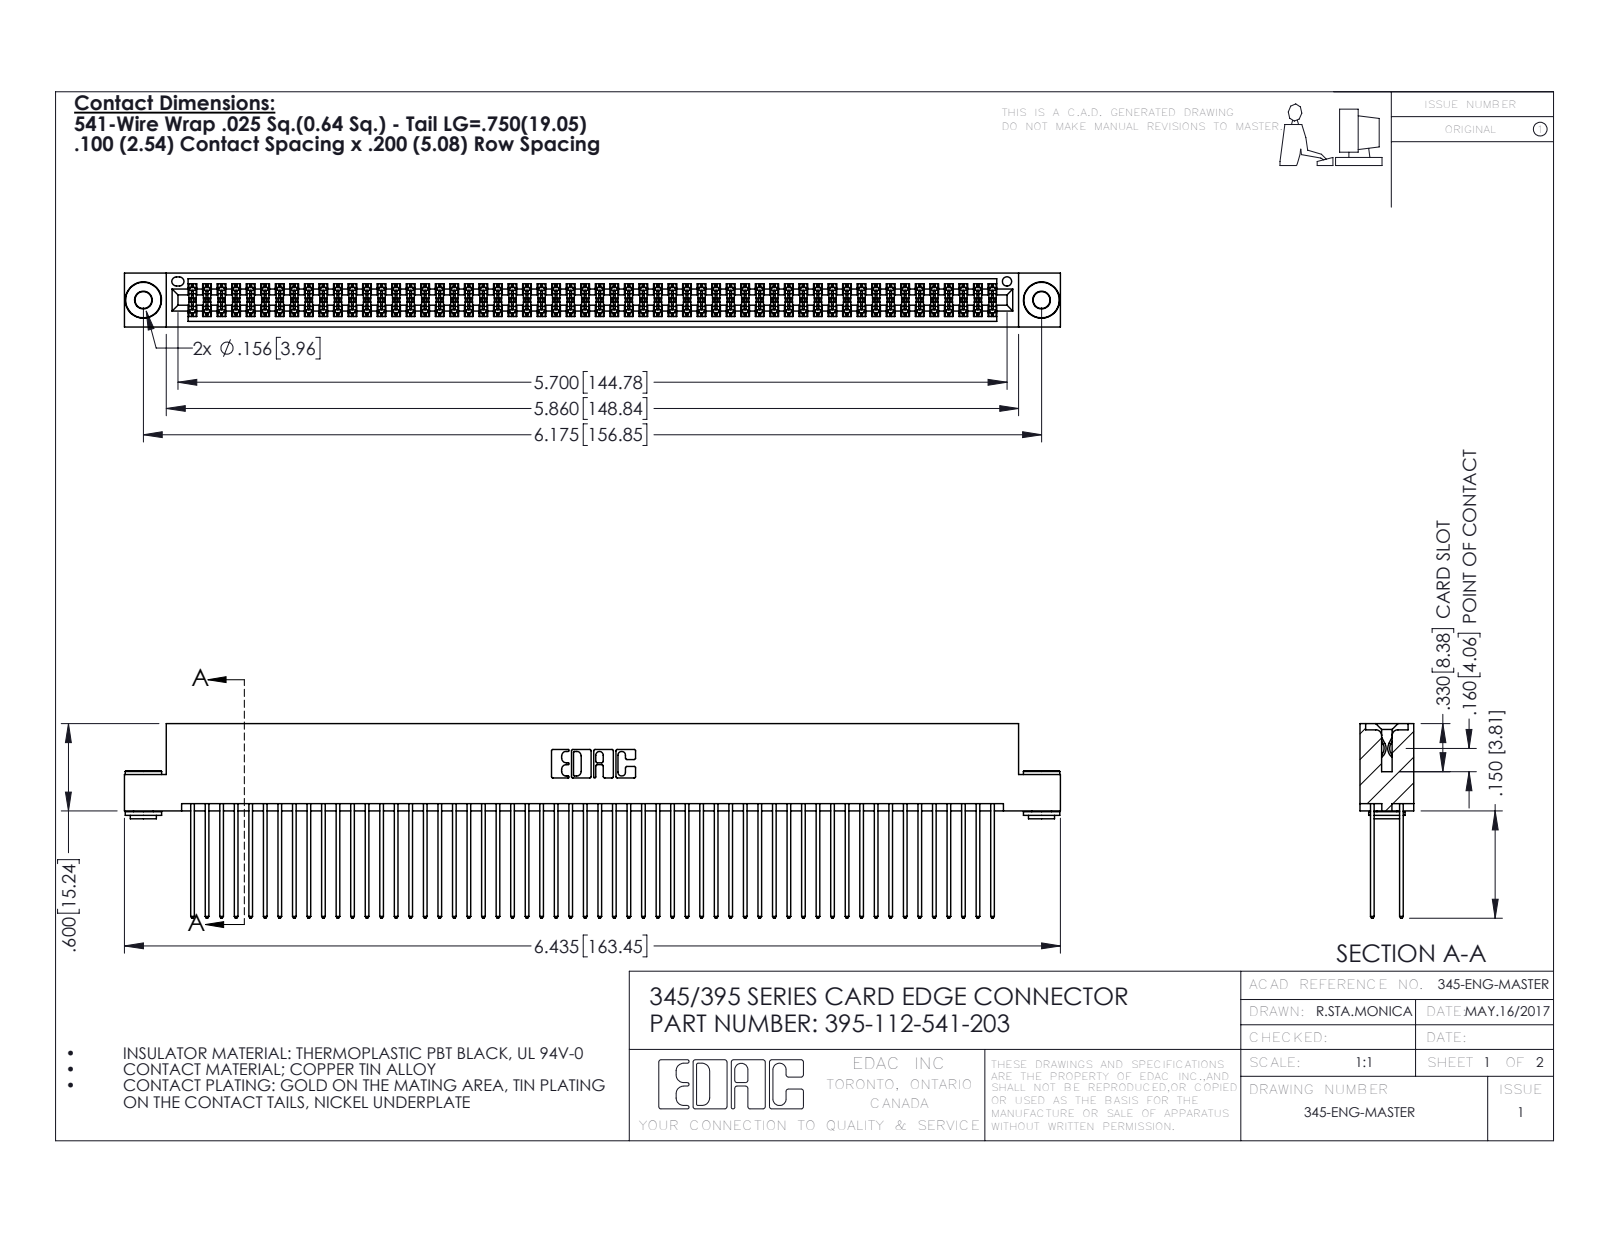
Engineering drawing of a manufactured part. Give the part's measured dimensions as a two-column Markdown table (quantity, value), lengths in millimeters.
| quantity | value |
| --- | --- |
| part name | 395-112-541-203; 345 Part_Flush Mounting Lugs - 0.156 Dia-TH; 345-250-002_345-250-002-102; 345-292-001_345-293-141 |
| STEP written by | SolidWorks 2016 (CONFIG_CONTROL_DESIGN) |
| units | millimeters |
| bodies | 115 solids, 5764 faces (3786 planar, 1970 cylindrical, 8 other) |
| overall size | 163.4 × 34 × 9.4 |
| volume | 16 670 mm³ |
| surface area | 28 140 mm² |
| round holes (diameter × count) | 2.9 × 2, 4 × 2, 1.6 × 1 |
| round bosses / shafts (diameter × count) | 6.4 × 2, 4.6 × 2, 3.5 × 2 |
| partial cylindrical surfaces (radius × count) | 0.2 × 168, 0.3 × 112, 0.3 × 22, 0.2 × 6, 0.8 × 6, 0.7 × 3, 0.4 × 2, 0.5 × 2 |
| main face-to-face distances | 1.8, 7.6, 5.1, 0.6, 2.5, 6.9, 5.7, 9.4, 4.4, 3.8 |
| hole center spacings | 6.9, 150.9, 156.8 |
